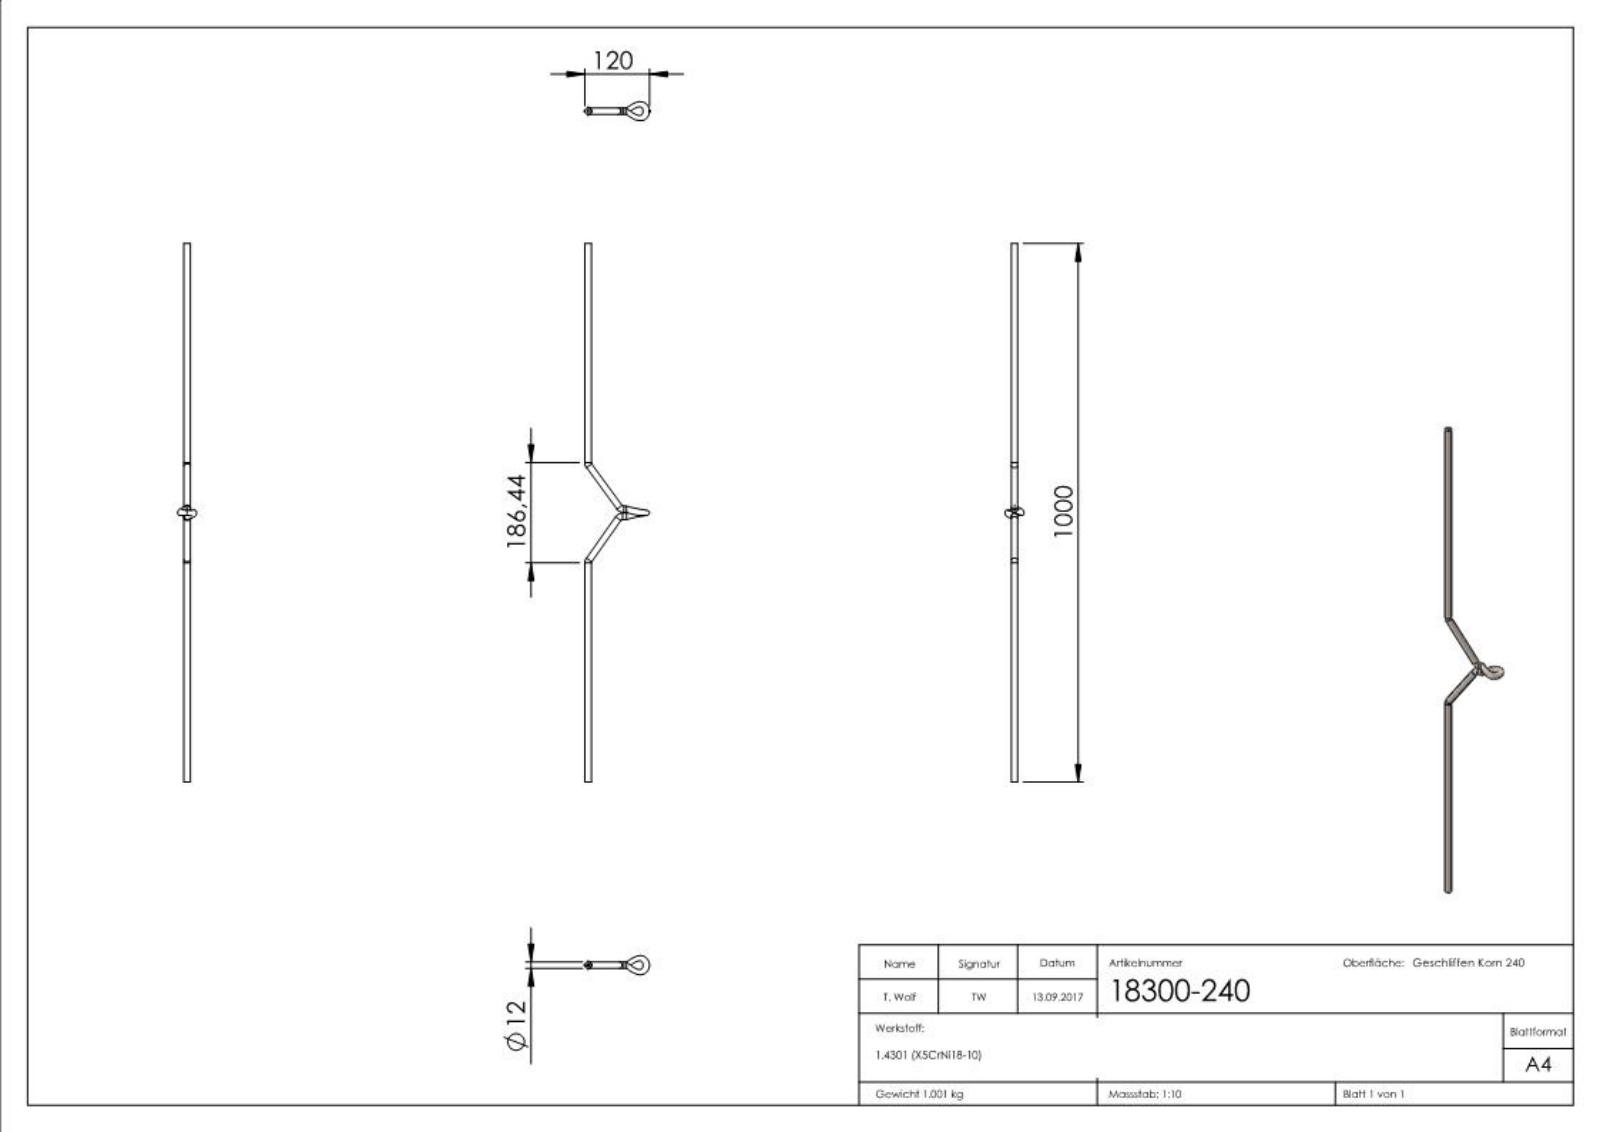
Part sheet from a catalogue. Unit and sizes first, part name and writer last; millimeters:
Units: millimetres
Overall size (bounding box): 1000 × 120.02 × 35.37
Round bosses / shafts (diameter × count): ⌀12 ×5
Main face-to-face distances: 1000, 0.5, 1.19, 0.66, 0.45, 1.35, 999.5, 0.55, 1.31, 0.85
Volume: 126 706 mm³ · Surface area: 42 930 mm²
Bodies: 1 solid, 137 faces (67 planar, 12 cylindrical, 58 other)
Part name (STEP PRODUCT): 18300-240
STEP written by: SolidWorks 2015 (CONFIG_CONTROL_DESIGN)
